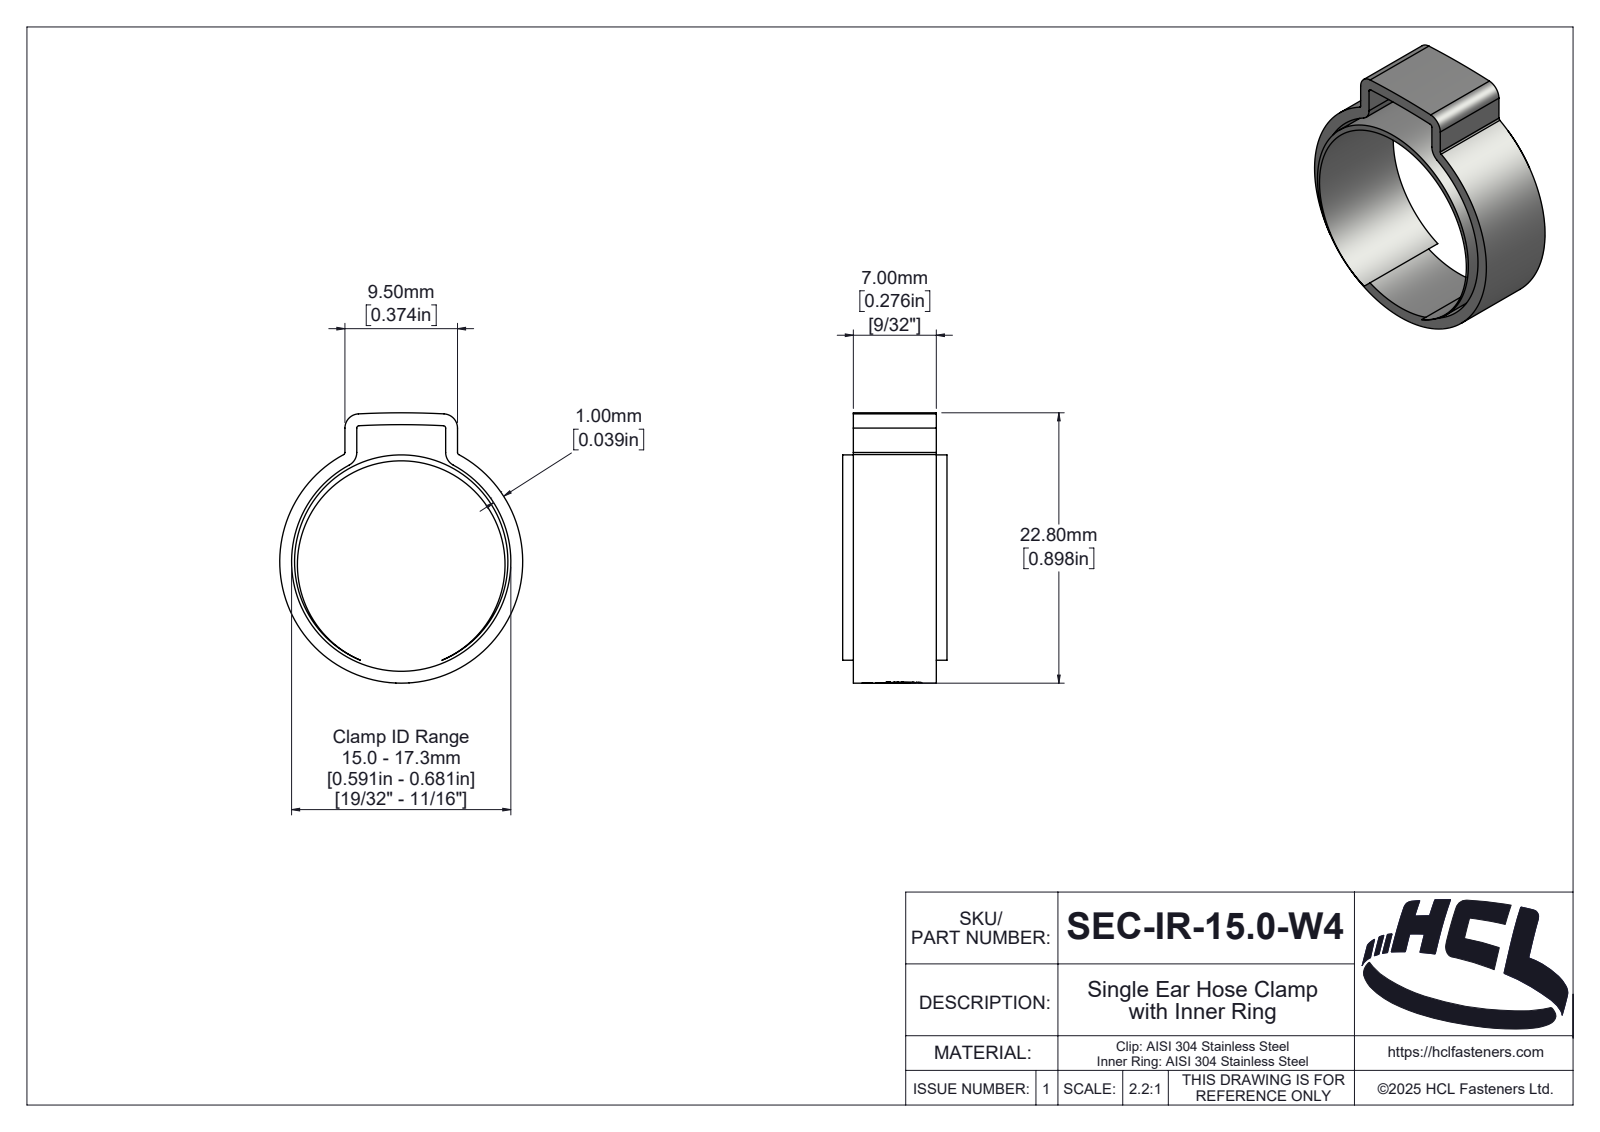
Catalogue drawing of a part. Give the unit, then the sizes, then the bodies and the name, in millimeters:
Units: millimetres
Overall size (bounding box): 22.8 × 20.5 × 8.8
Round holes (diameter × count): ⌀17.52 ×1, ⌀18.5 ×1
Round bosses / shafts (diameter × count): ⌀20.5 ×1, ⌀18 ×1
Partial cylindrical surfaces — rounded edges, fillets, slot ends (radius × count): R0.2 ×4, R1.2 ×4, R0.21 ×1, R0.88 ×1, R1.09 ×1, R1.15 ×1, R1.39 ×1, R1.97 ×1
Main face-to-face distances: 7, 1, 8.5, 0.9, 7.9, 9.5, 7.5, 8.8, 4.46, 3.46
Volume: 584 mm³ · Surface area: 1 954 mm²
Bodies: 2 solids, 131 faces (10 planar, 72 cylindrical, 49 other)
Part name (STEP PRODUCT): SEC-IR-15.0-W4
STEP written by: SolidWorks 2025 (AUTOMOTIVE_DESIGN)
